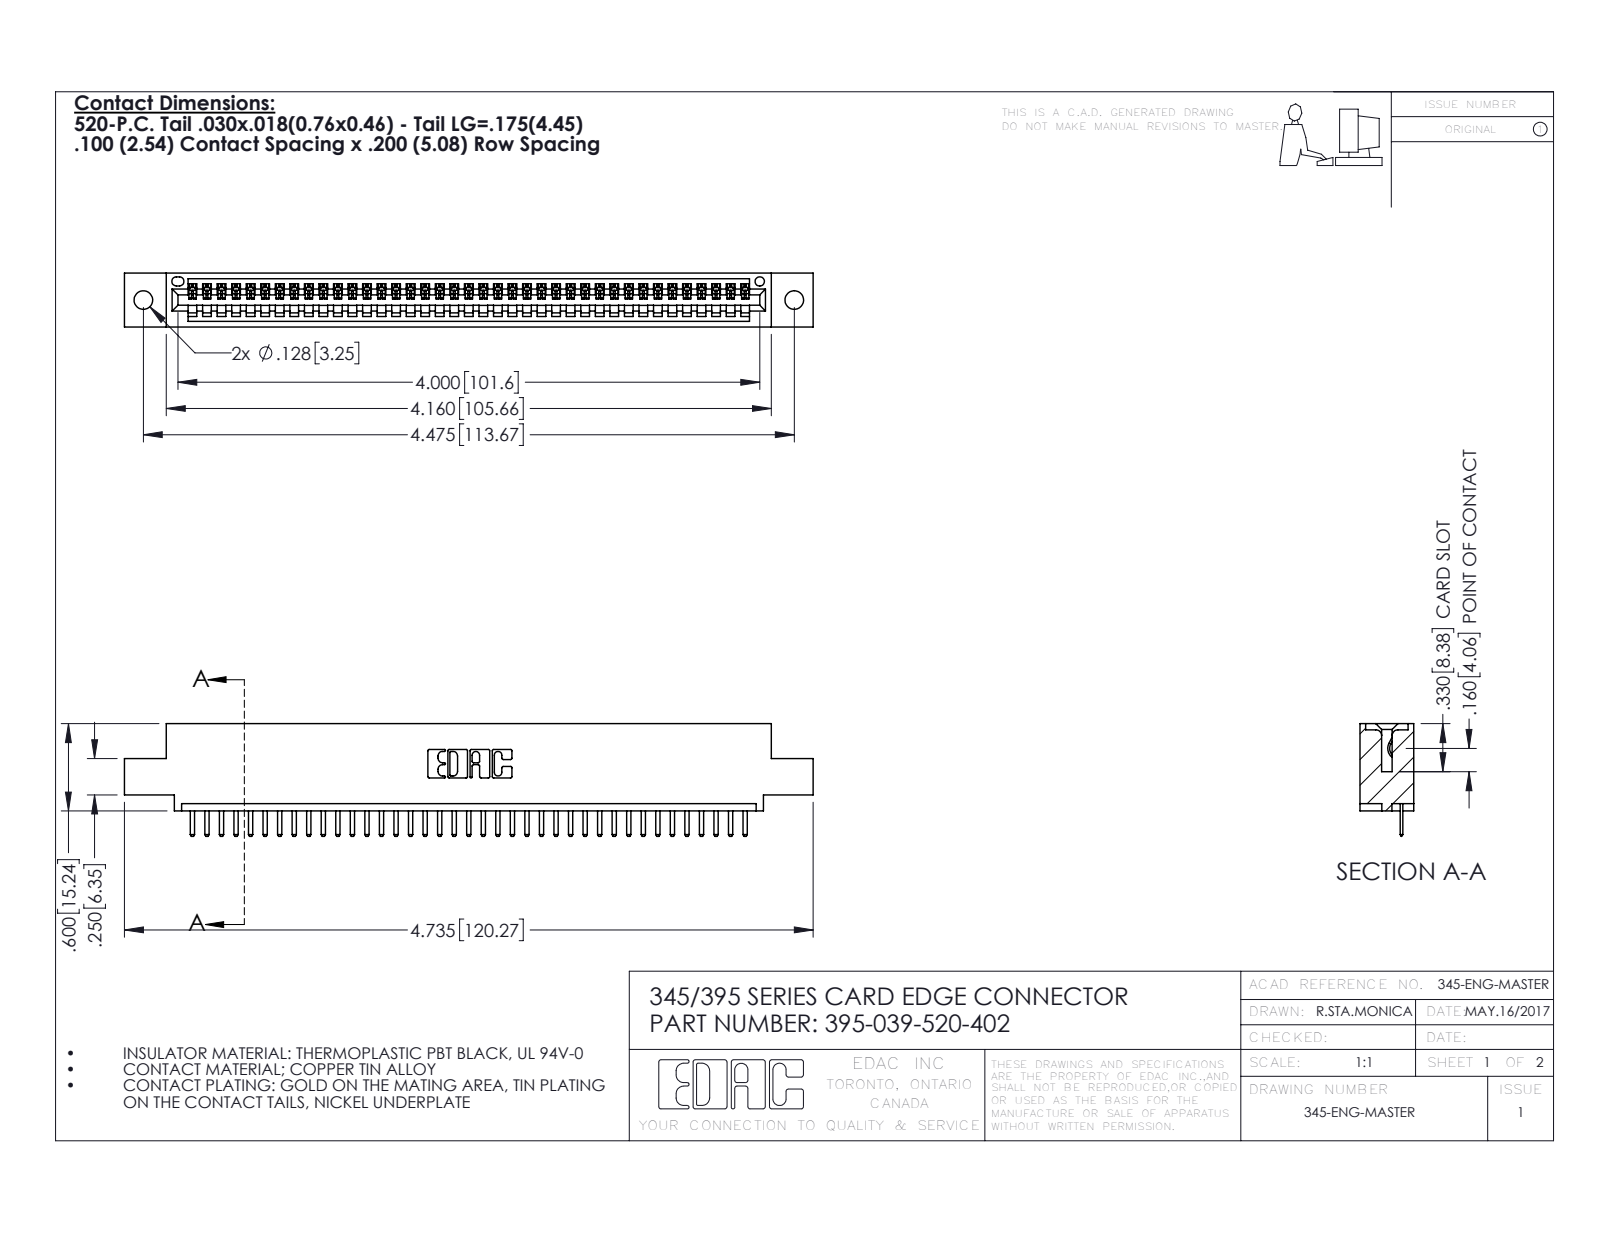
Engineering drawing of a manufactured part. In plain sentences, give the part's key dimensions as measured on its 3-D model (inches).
The part is named "345-292-001_345-293-120; 345 Part_0.110 Offset - 0.128 Dia; 395-039-520-402". Its 3-D file was written by "SolidWorks 2016 (CONFIG_CONTROL_DESIGN)". It is 40 solids with 2548 faces: 1722 planar, 826 cylindrical and 0 other. Overall it measures 4.735 by 0.775 by 0.37 inches. Its volume is 0.682 cubic inches and its surface area 22.1 square inches. Round holes: 2 of diameter 0.128, 1 of diameter 0.064. Partial cylindrical surfaces (rounded edges, fillets, slot ends): 80 of radius 0.01, 78 of radius 0.006, 22 of radius 0.01, 6 of radius 0.007, 6 of radius 0.031, 3 of radius 0.026, 2 of radius 0.031, 2 of radius 0.04. The main face-to-face distances are 0.298, 0.072, 0.37, 0.2, 0.098, 0.272, 0.025, 0.225, 0.072, 0.149. The hole center spacings are 0.27, 4.239, 4.475.
